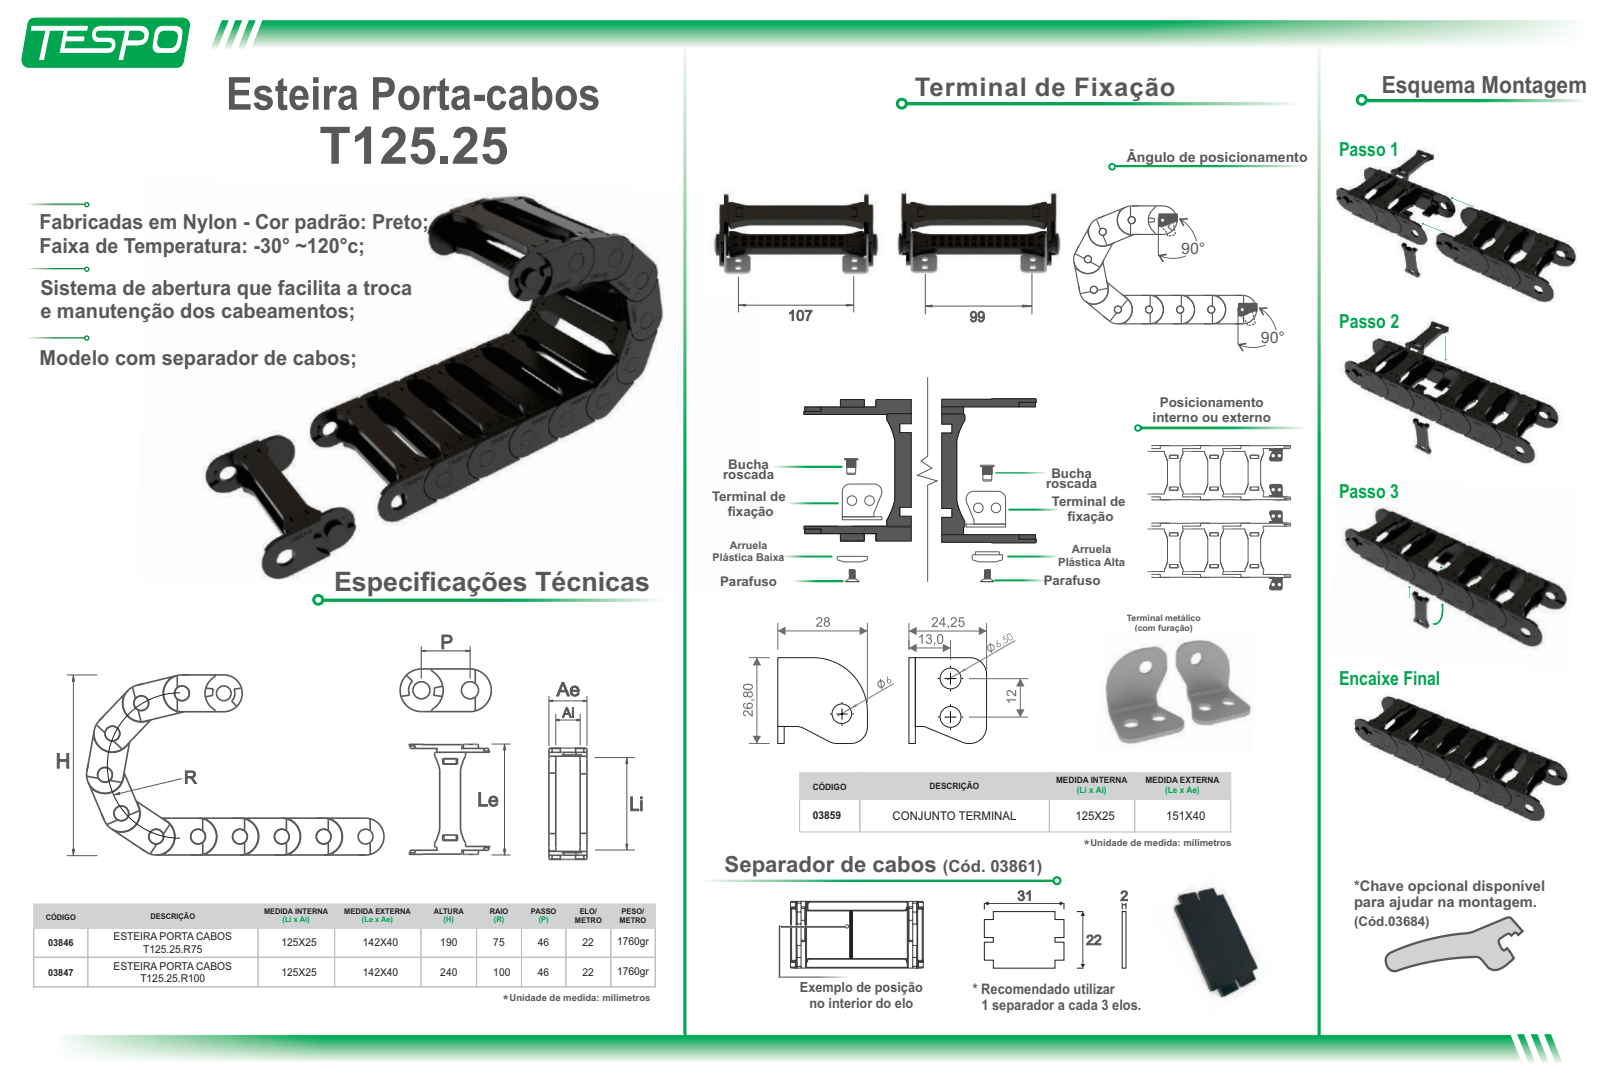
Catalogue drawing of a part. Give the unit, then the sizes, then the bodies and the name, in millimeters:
Units: millimetres
Overall size (bounding box): 141.78 × 85.5 × 40
Main face-to-face distances: 4.05, 133.08, 7.2, 32.8, 129.03, 40, 8.1, 137.13, 25.6, 124.98
Volume: 70 893 mm³ · Surface area: 34 507 mm²
Bodies: 4 solids, 155 faces (92 planar, 0 cylindrical, 63 other)
STEP written by: ST-DEVELOPER v15 (AUTOMOTIVE_DESIGN)
